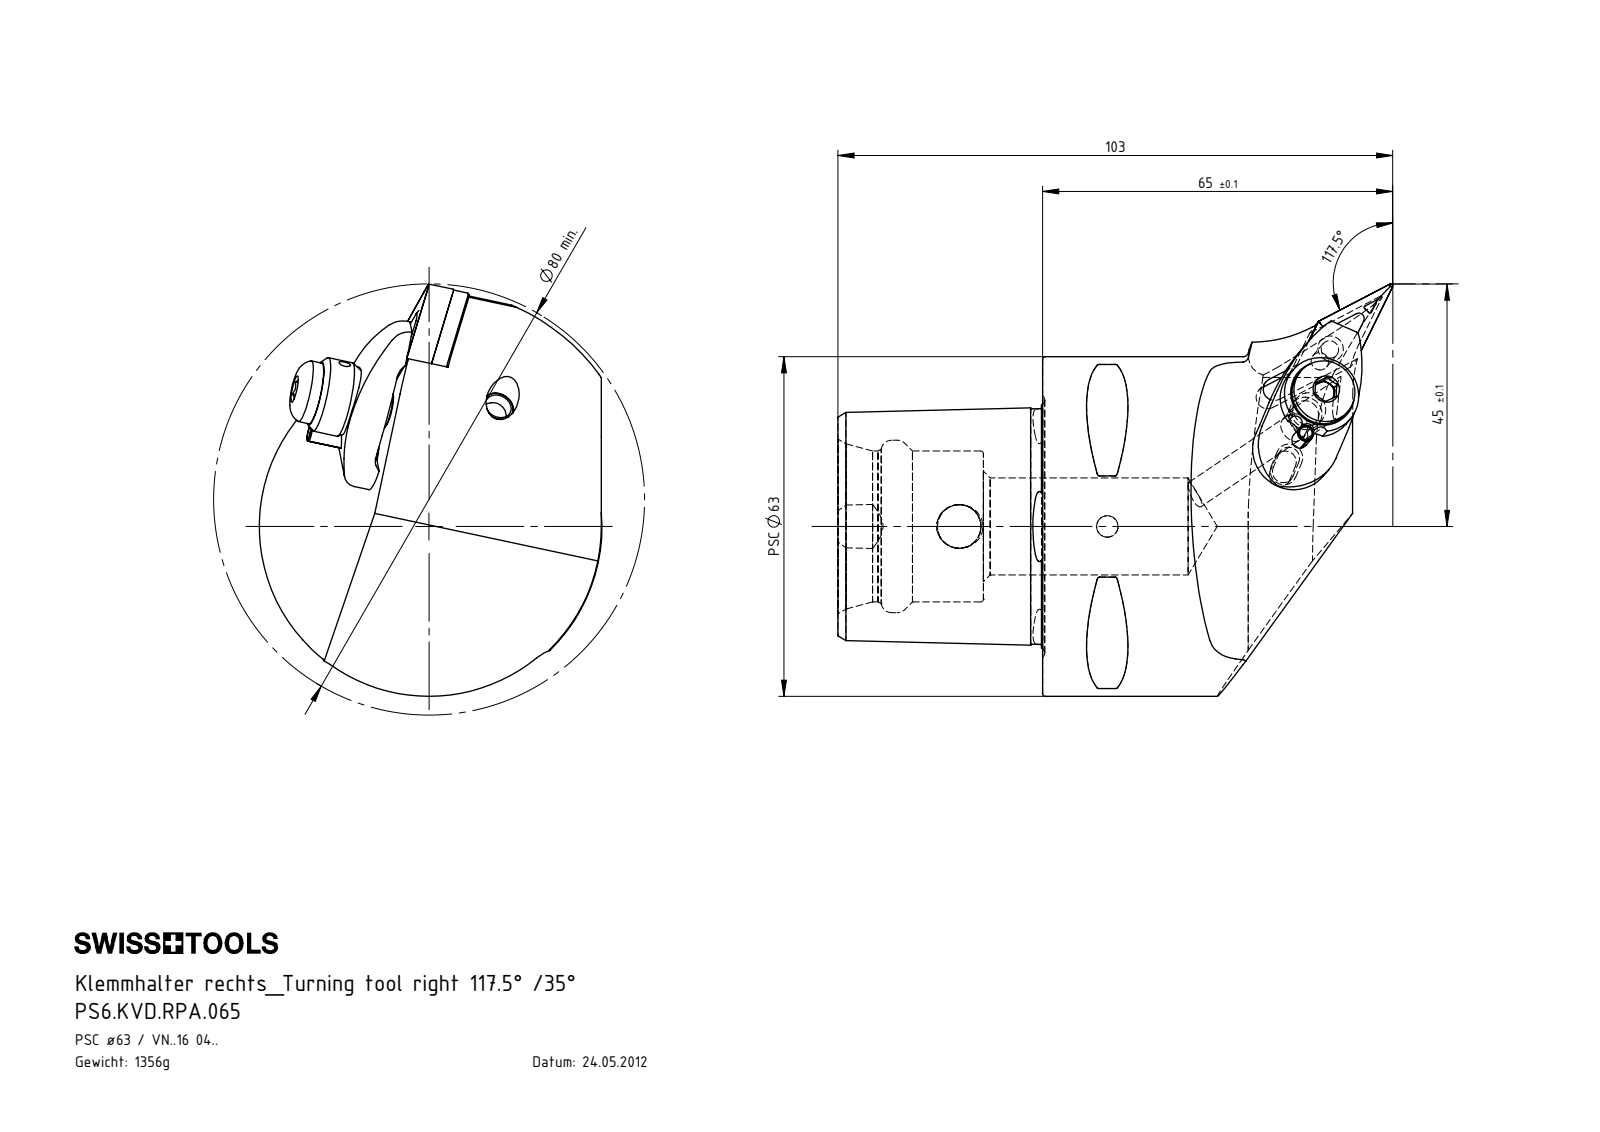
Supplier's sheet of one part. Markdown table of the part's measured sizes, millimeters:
| quantity | value |
| --- | --- |
| part name | PS6.KVD.RPA.065; WCC-ER4.103.032_A; PS6-KVD.RPA.065_A; WCC-ER5.102.012_B (+7 more) |
| STEP written by | SolidWorks 2017 (AUTOMOTIVE_DESIGN) |
| units | millimeters |
| bodies | 11 solids, 429 faces (100 planar, 132 cylindrical, 197 other) |
| overall size | 103 × 76.5 × 63.61 |
| volume | 172 190 mm³ |
| surface area | 32 965 mm² |
| round holes (diameter × count) | 2 × 3, 5 × 3, 7 × 2, 2.4 × 1, 3 × 1, 3.3 × 1, 3.8 × 1, 4 × 1, 4.95 × 1, 6 × 1, 6.2 × 1, 6.9 × 1 |
| round bosses / shafts (diameter × count) | 6 × 2, 3 × 2, 63 × 1, 14 × 1, 11.5 × 1, 7 × 1, 6.8 × 1, 6.2 × 1 |
| partial cylindrical surfaces (radius × count) | 0.5 × 10, 0.39 × 6, 0.4 × 4, 0.69 × 3, 0.69 × 3, 1.5 × 3, 6 × 3, 2 × 2 |
| main face-to-face distances | 38, 24.88, 4.44, 27, 11, 1.31, 5.75, 7.62, 55.8, 9.52 |
| hole center spacings | 8.02, 8, 8.03, 8.19, 8.21, 14.02, 14.12, 14.2 |
